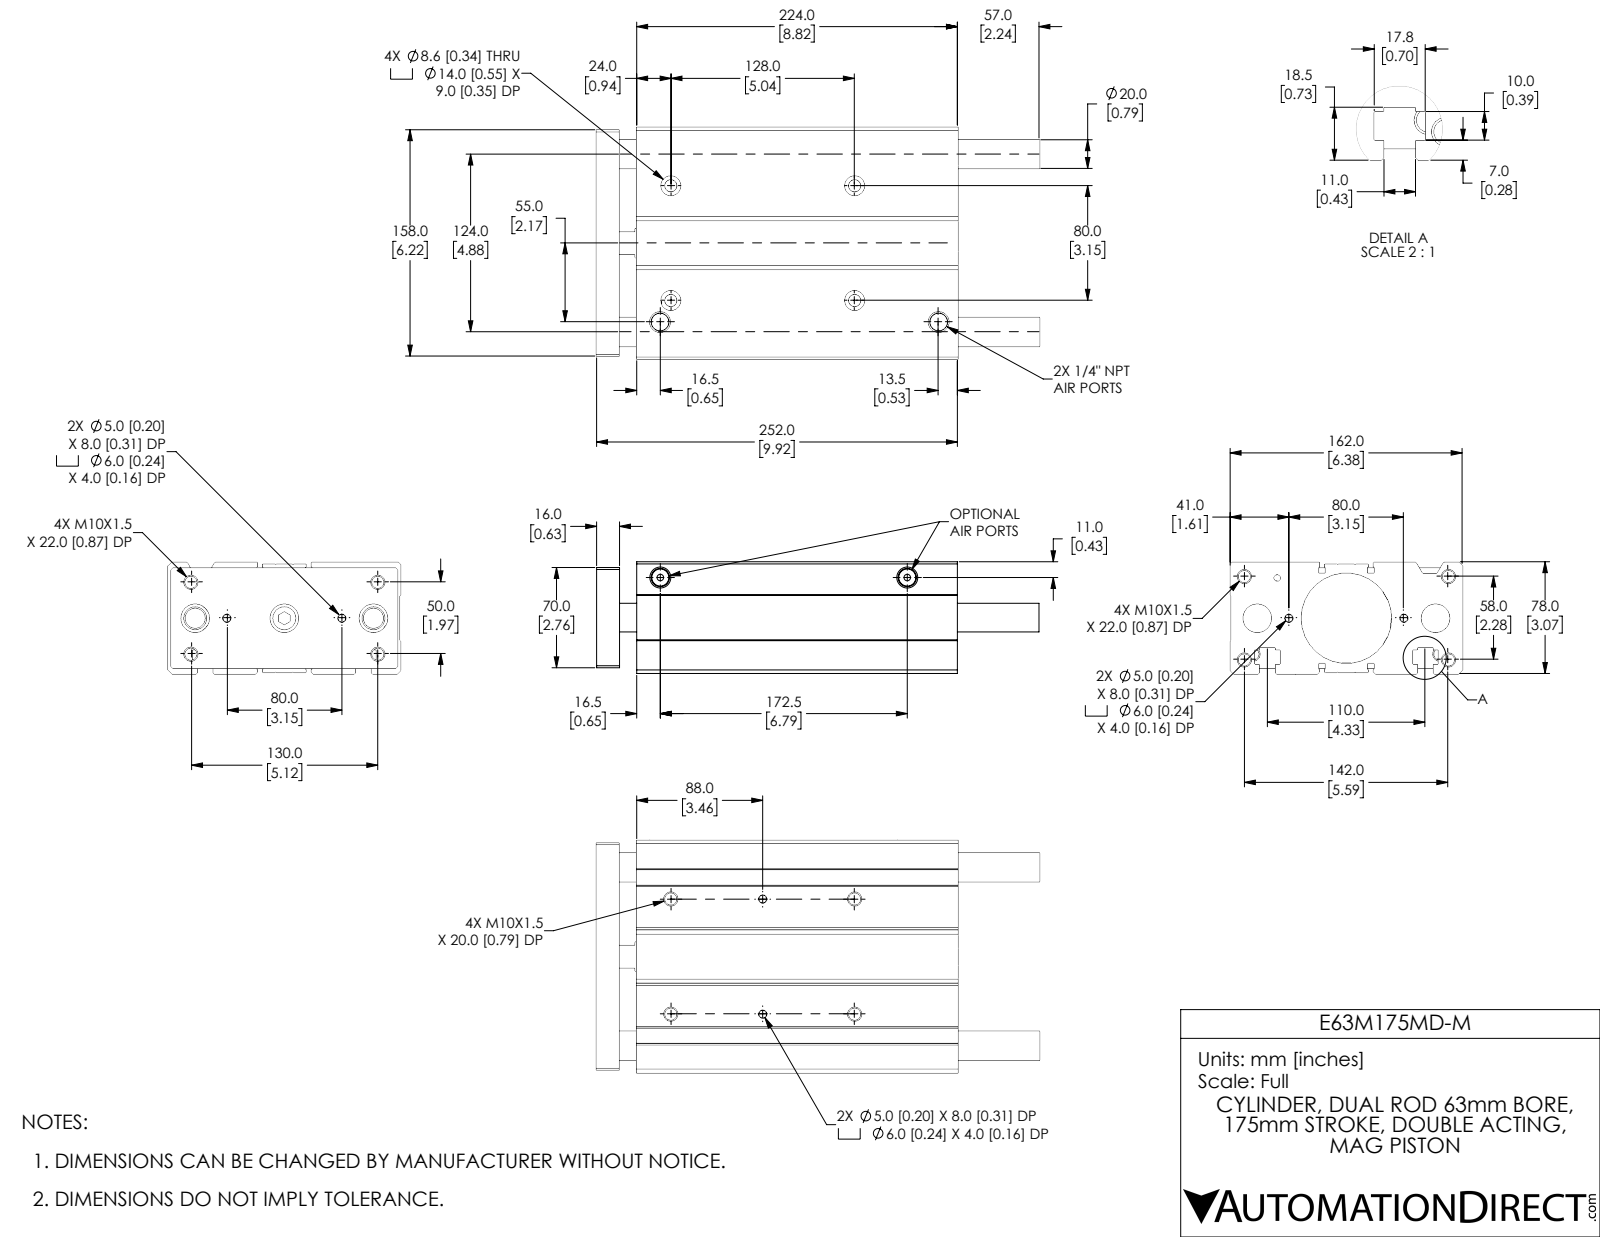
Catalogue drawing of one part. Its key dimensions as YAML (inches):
part_name: "E63M175MD-M; E63M175MD-M_BODY; E63M175MD-M_ENDPLATE"
step_written_by: "SolidWorks 2019 (CONFIG_CONTROL_DESIGN)"
units: inches
bodies: {solids: 5, faces: 421, planar: 139, cylindrical: 190, other: 92}
overall_size: [12.165, 6.378, 3.071]
volume: 141.4
surface_area: 550.9
round_holes:
  - {diameter: 0.33, count: 12}
  - {diameter: 0.197, count: 4}
  - {diameter: 0.236, count: 4}
  - {diameter: 0.339, count: 4}
  - {diameter: 0.551, count: 4}
  - {diameter: 0.18, count: 3}
  - {diameter: 0.394, count: 3}
  - {diameter: 0.787, count: 3}
  - {diameter: 0.63, count: 2}
  - {diameter: 0.787, count: 1}
  - {diameter: 2.48, count: 1}
  - {diameter: 2.48, count: 1}
round_bosses_or_shafts:
  - {diameter: 0.63, count: 1}
partial_cylinders:
  - {radius: 0.008, count: 32}
  - {radius: 0.016, count: 28}
  - {radius: 0.059, count: 4}
  - {radius: 0.012, count: 2}
face_to_face_distances: [3.071, 0.047, 3.024, 1.102, 0.63, 0.472, 0.024, 0.157, 6.378, 9.921]
hole_center_spacings: [0.284, 0.991, 1.195, 1.392, 1.671, 2.139, 2.52, 2.742]
